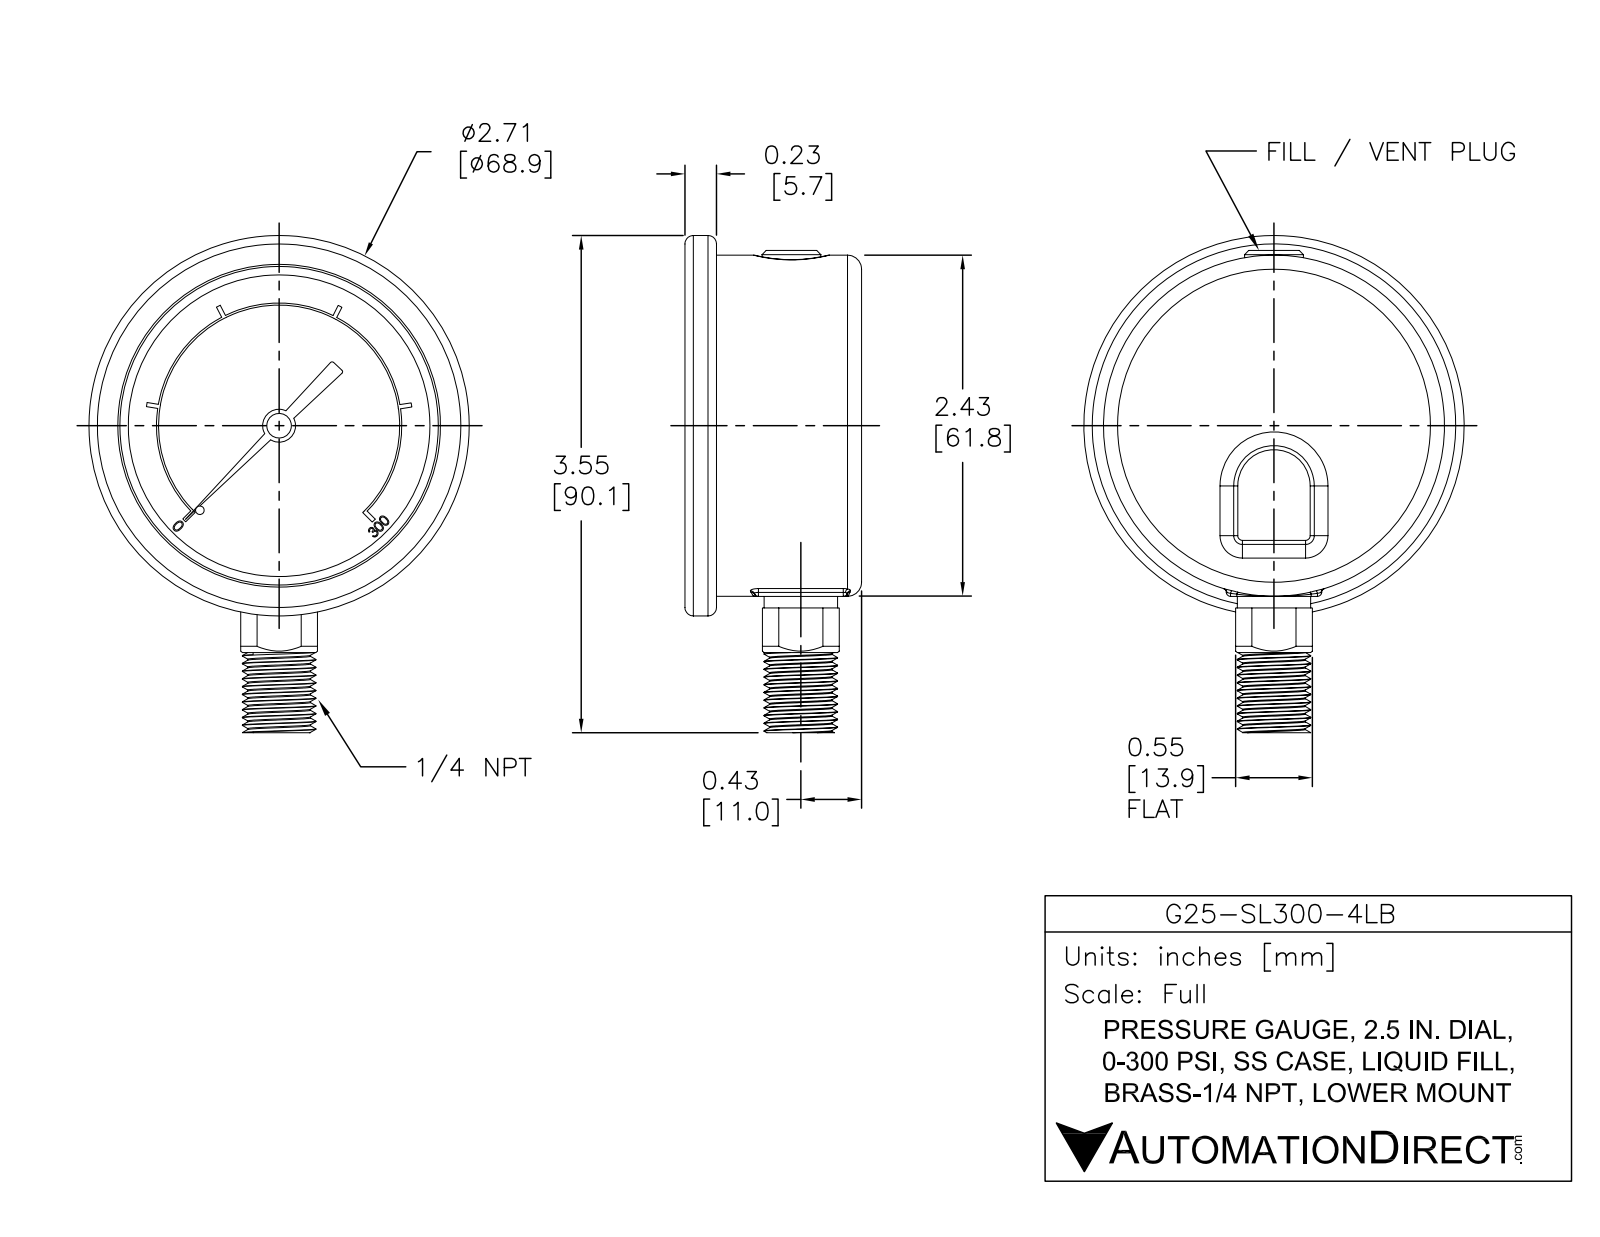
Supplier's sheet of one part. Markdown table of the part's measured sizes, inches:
| quantity | value |
| --- | --- |
| part name | G25-SL300-4LB |
| STEP written by | SolidWorks 2021 (AUTOMOTIVE_DESIGN) |
| units | inches |
| bodies | 1 solid, 354 faces (192 planar, 85 cylindrical, 77 other) |
| overall size | 3.546 × 2.713 × 1.26 |
| volume | 5.273 in³ |
| surface area | 24.68 in² |
| round holes (diameter × count) | 0.027 × 1, 0.071 × 1, 0.119 × 1, 2.272 × 1 |
| round bosses / shafts (diameter × count) | 2.713 × 1, 2.433 × 1, 0.524 × 1, 0.42 × 1, 0.235 × 1, 0.176 × 1, 0.14 × 1, 0.041 × 1 |
| partial cylindrical surfaces (radius × count) | 0.03 × 9, 0.1 × 3, 0.015 × 2, 0.316 × 1, 0.86 × 1, 0.875 × 1 |
| main face-to-face distances | 1.01, 1.26, 0.25, 1.035, 0.025, 0.225, 0.1, 0.91, 0.935, 1.16 |
| hole center spacings | 0.067 |
